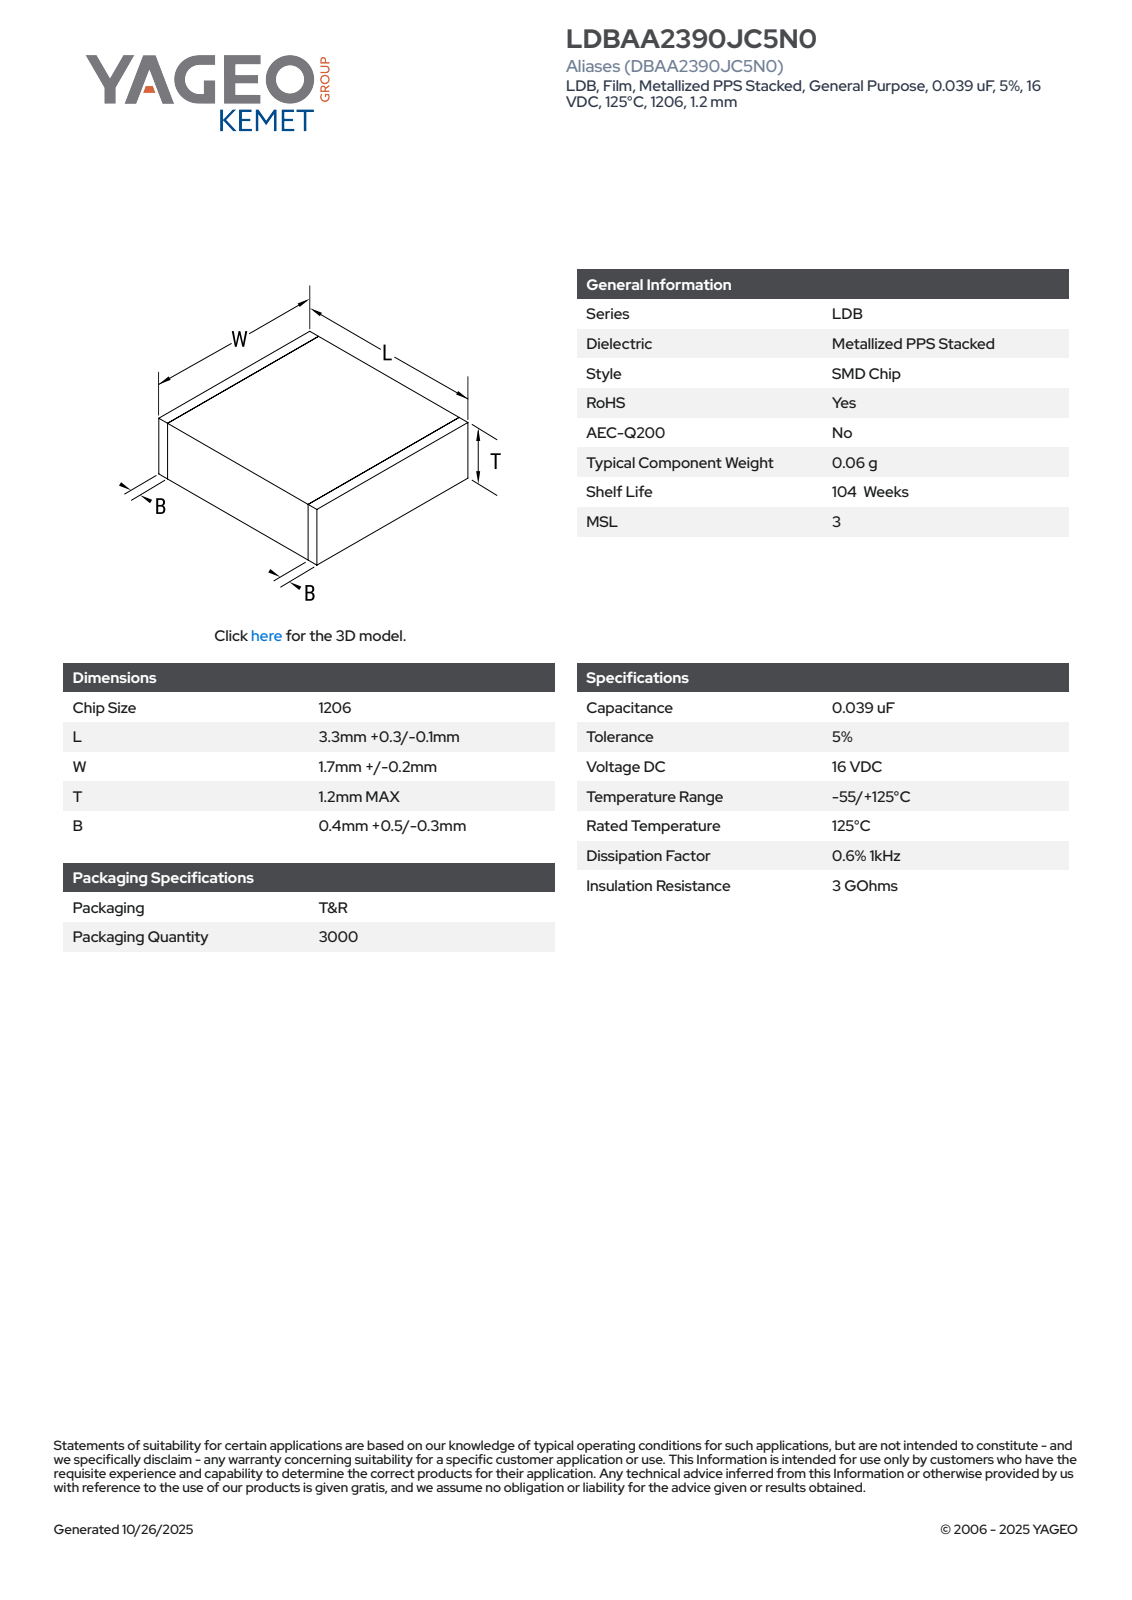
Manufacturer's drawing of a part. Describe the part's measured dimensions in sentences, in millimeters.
The part is named "CFS_LDELDB_1206_L3.6W1.9T1.2B0.9". Its 3-D file was written by "SolidWorks 2020 (AUTOMOTIVE_DESIGN)". It is 4 solids with 73 faces: 73 planar, 0 cylindrical and 0 other. Overall it measures 3.6 by 1.9 by 1.2 millimeters. Its volume is 8 cubic millimeters and its surface area 27 square millimeters. The main face-to-face distances are 1.18, 1.19, 1.88, 1.89, 3.6, 1.2, 1.9, 0.5, 3.1, 2.6.
